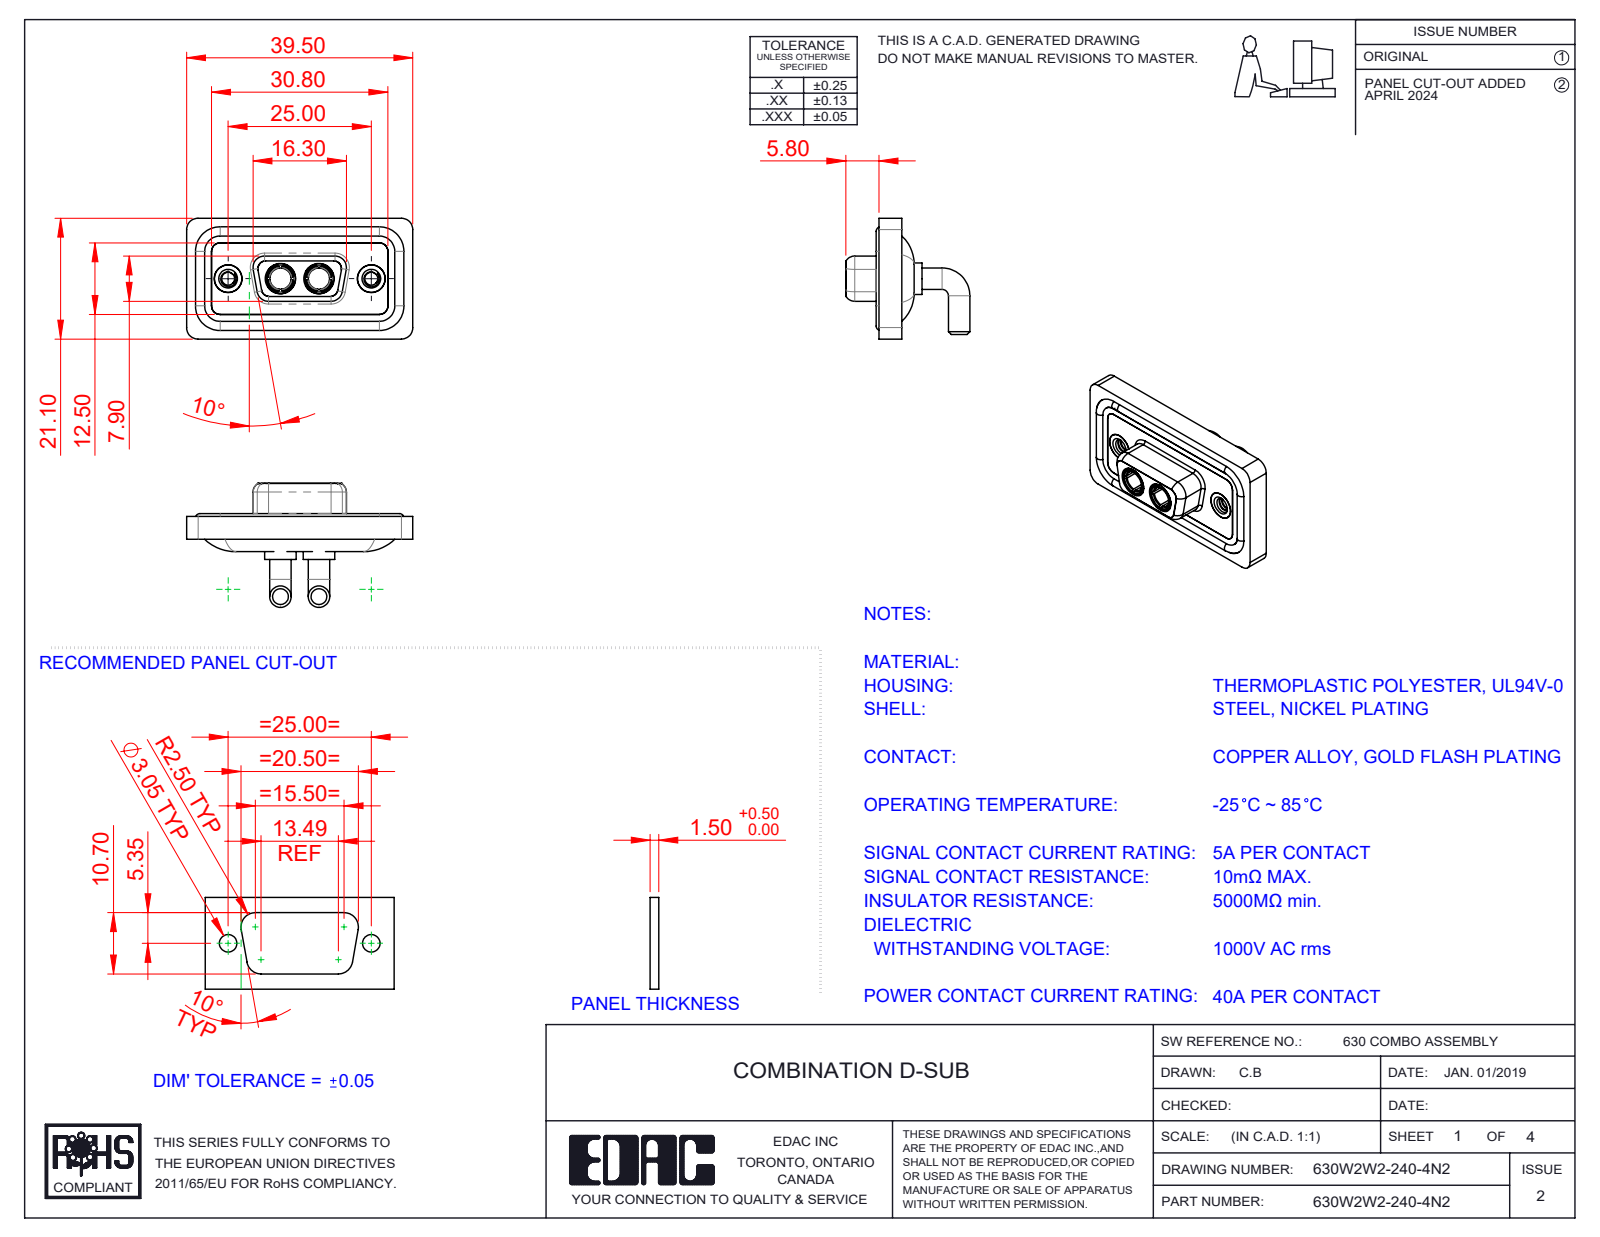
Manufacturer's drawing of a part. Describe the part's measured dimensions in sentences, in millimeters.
The part is named "630Combo Shell Rear_09 Contacts; Power Socket_40A RA; 630Combo Waterproof Housing_09 Contacts; 630Combo Shell Front_09 Contacts (+3 more)". Its 3-D file was written by "SolidWorks 2023 (CONFIG_CONTROL_DESIGN)". It is 11 solids with 542 faces: 163 planar, 238 cylindrical and 141 other. Overall it measures 39.5 by 21.68 by 21.1 millimeters. Its volume is 4 961 cubic millimeters and its surface area 7 873 square millimeters. Round holes: 4 of diameter 4.85, 2 of diameter 2.26, 2 of diameter 3.7, 2 of diameter 4, 2 of diameter 4.05, 2 of diameter 5, 2 of diameter 5.3. Round bosses or shafts: 4 of diameter 3.75, 4 of diameter 1.6, 2 of diameter 5.5, 2 of diameter 5.2, 2 of diameter 4.96, 2 of diameter 4.95, 2 of diameter 4.8, 2 of diameter 4.75. Partial cylindrical surfaces (rounded edges, fillets, slot ends): 18 of radius 1.5, 18 of radius 2, 8 of radius 1.35, 8 of radius 1.6, 4 of radius 0.25, 4 of radius 0.5, 4 of radius 0.6, 4 of radius 0.65. The main face-to-face distances are 0.4, 1.8, 1.1, 2.9, 2.5, 1.6, 3.1, 2.1, 0.5, 3.7. The hole center spacings are 9.14, 15.86, 6.72, 25.
